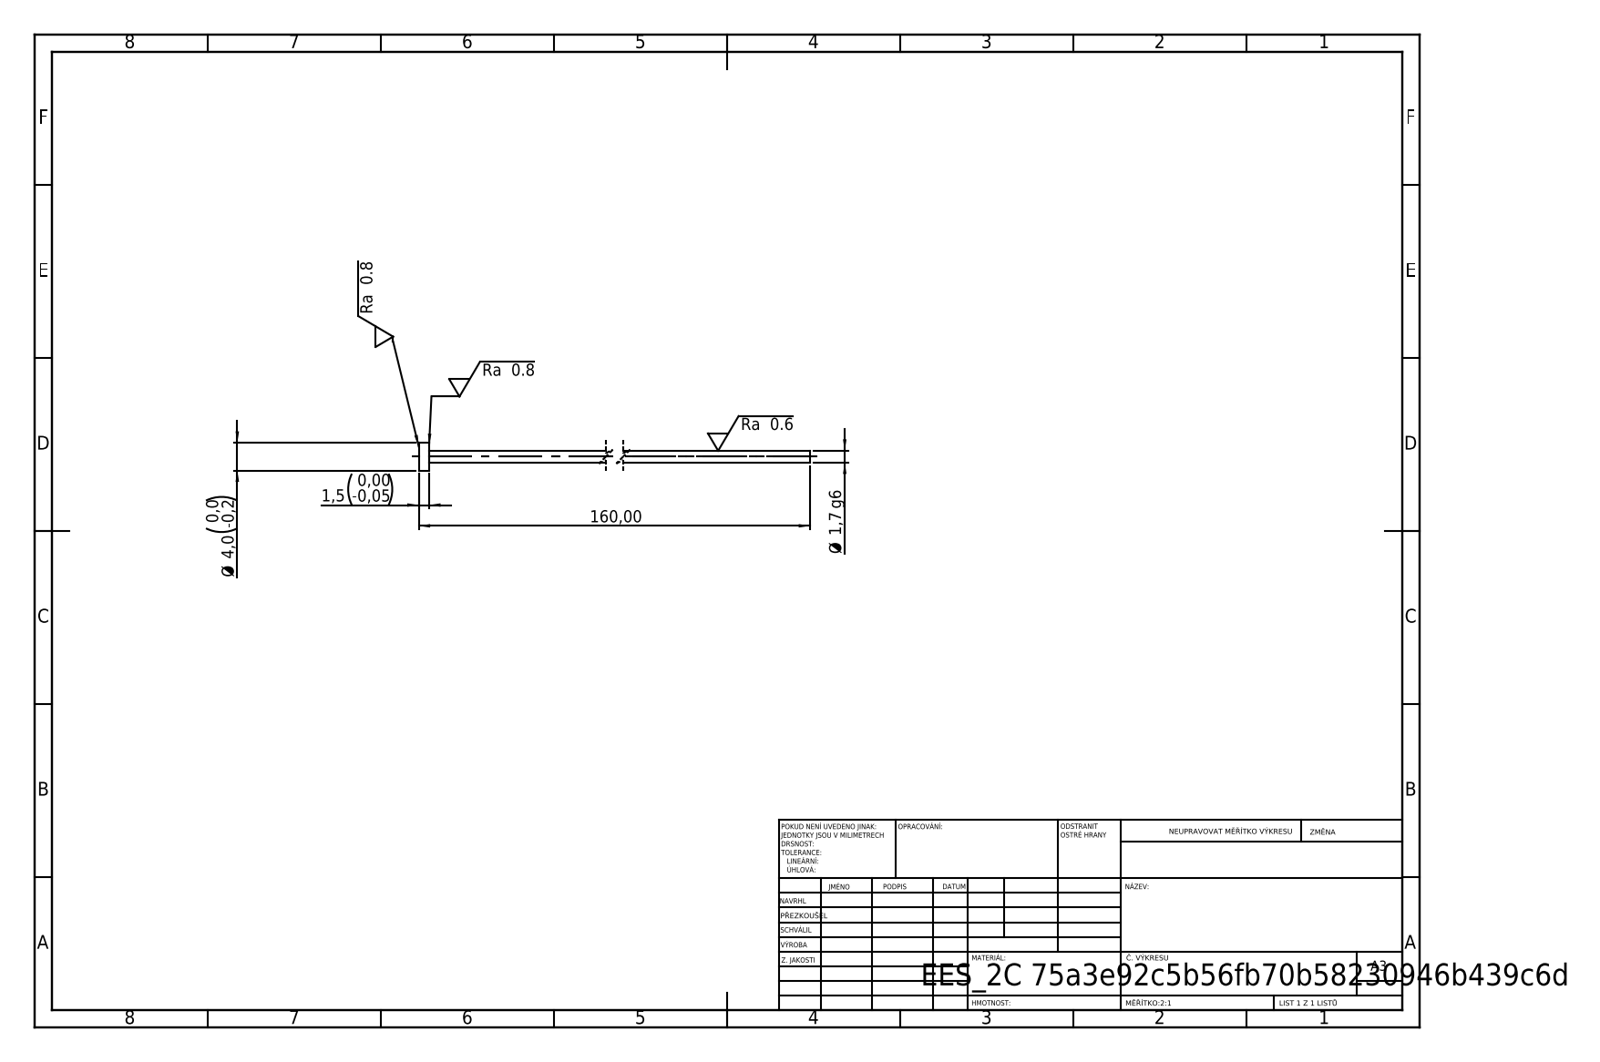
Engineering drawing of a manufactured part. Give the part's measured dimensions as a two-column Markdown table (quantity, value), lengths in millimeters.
| quantity | value |
| --- | --- |
| STEP written by | SolidWorks 2019 (CONFIG_CONTROL_DESIGN) |
| units | millimeters |
| bodies | 1 solid, 7 faces (3 planar, 4 cylindrical, 0 other) |
| overall size | 160 × 4 × 4 |
| volume | 379 mm³ |
| surface area | 890 mm² |
| round bosses / shafts (diameter × count) | 4 × 1, 1.7 × 1 |
| main face-to-face distances | 1.5, 160, 158.5 |
